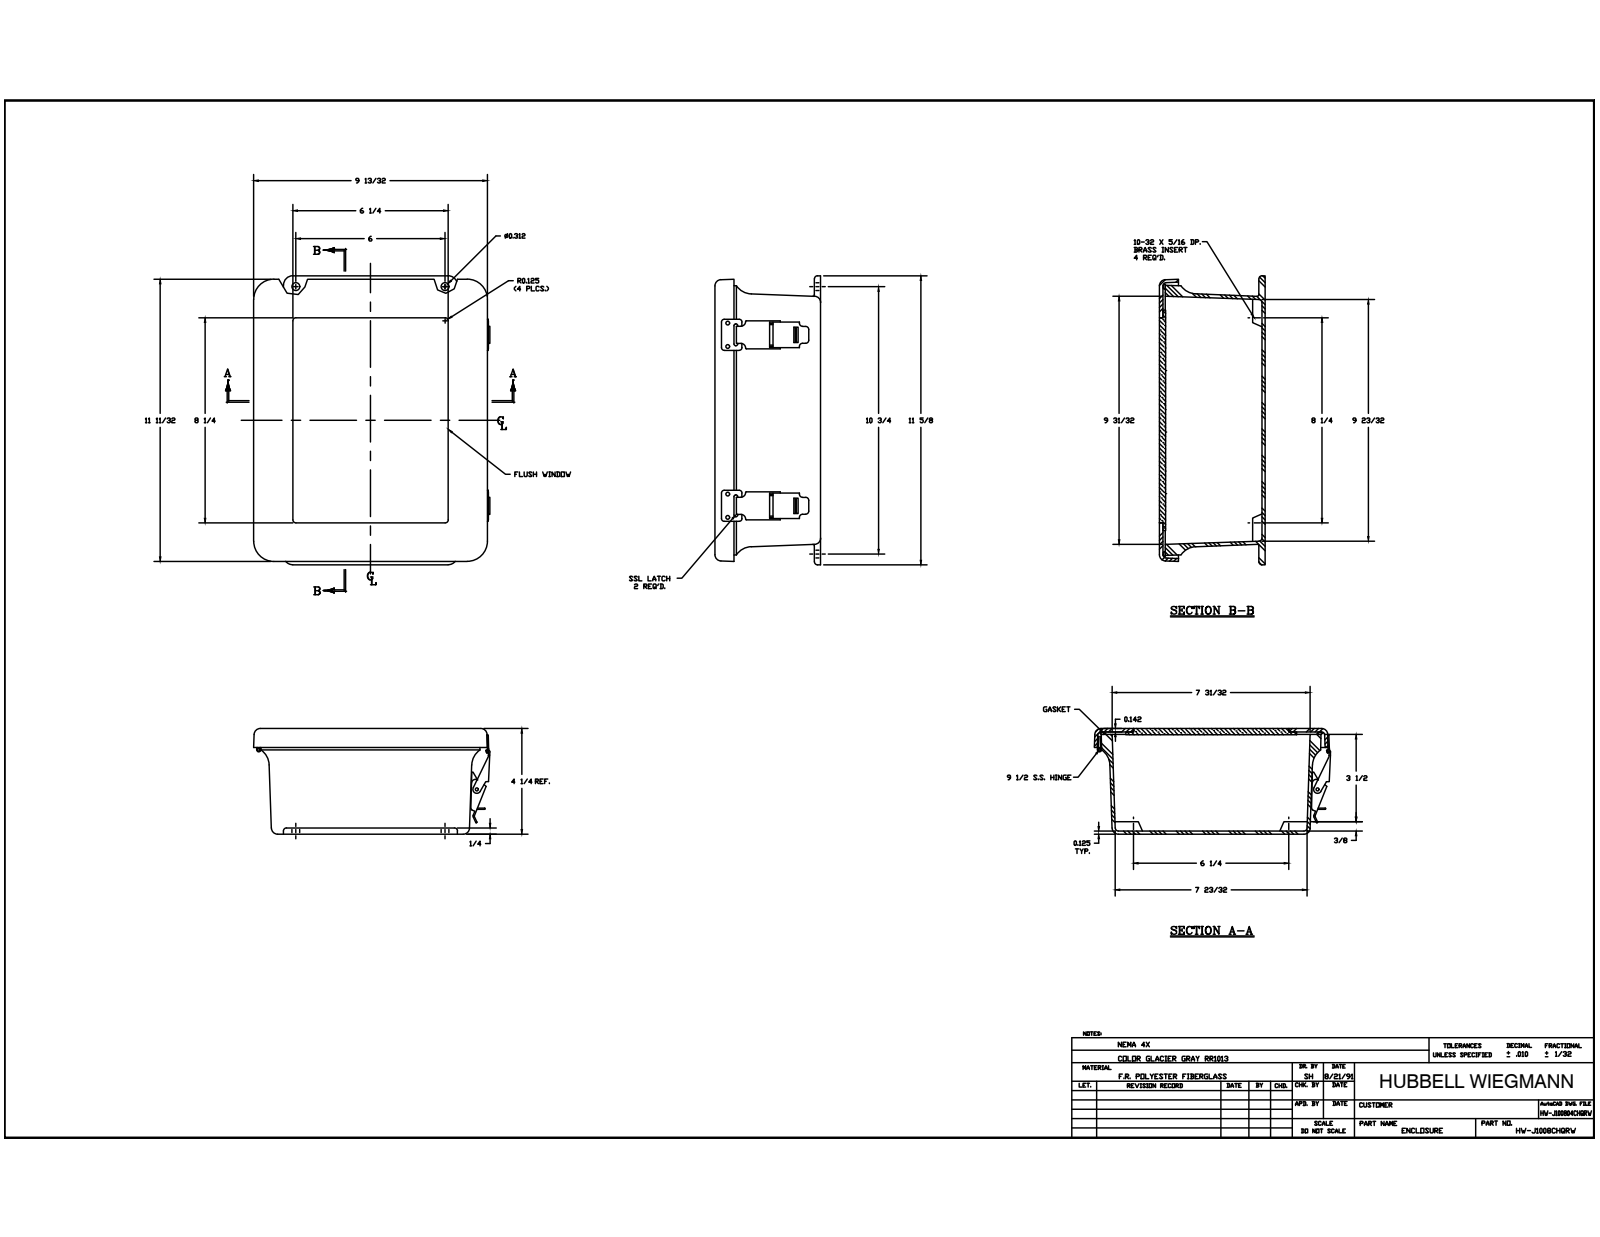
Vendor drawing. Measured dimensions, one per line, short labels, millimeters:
name: J1008HL_4; RMINS45821P_69; RMINS45821P_70; RMINS45821P_71 (+8 more)
written by: Autodesk Inventor 2014 (AUTOMOTIVE_DESIGN)
unit: mm
bodies: 39 solids, 966 faces (414 planar, 405 cylindrical, 147 other)
size: 295.27 × 242.12 × 107.55
volume: 1 112 000 mm³; area: 560 061 mm²
holes: 20× ⌀3.56, 8× ⌀2.64, 8× ⌀3.33, 5× ⌀3.86, 4× ⌀3.3, 4× ⌀3.96, 4× ⌀5.54, 2× ⌀3.43, 2× ⌀9.52, 1× ⌀2.16, 1× ⌀2.16
bosses: 16× ⌀3.17, 8× ⌀6.35, 4× ⌀6.86, 1× ⌀7.62, 1× ⌀4.31, 1× ⌀3.94, 1× ⌀3.05
rounds: 24× R3.17, 20× R0.38, 20× R0.79, 16× R1.14, 12× R0.76, 12× R6.35, 9× R0.57, 6× R1.52
face distances: 107.55, 6.35, 101.2, 103.94, 3.61, 3.17, 100.77, 104.38, 98.03, 2.74
hole spacings: 177.8, 178.82, 23.81, 152.4, 19.05, 76.2, 6.35, 19.04
